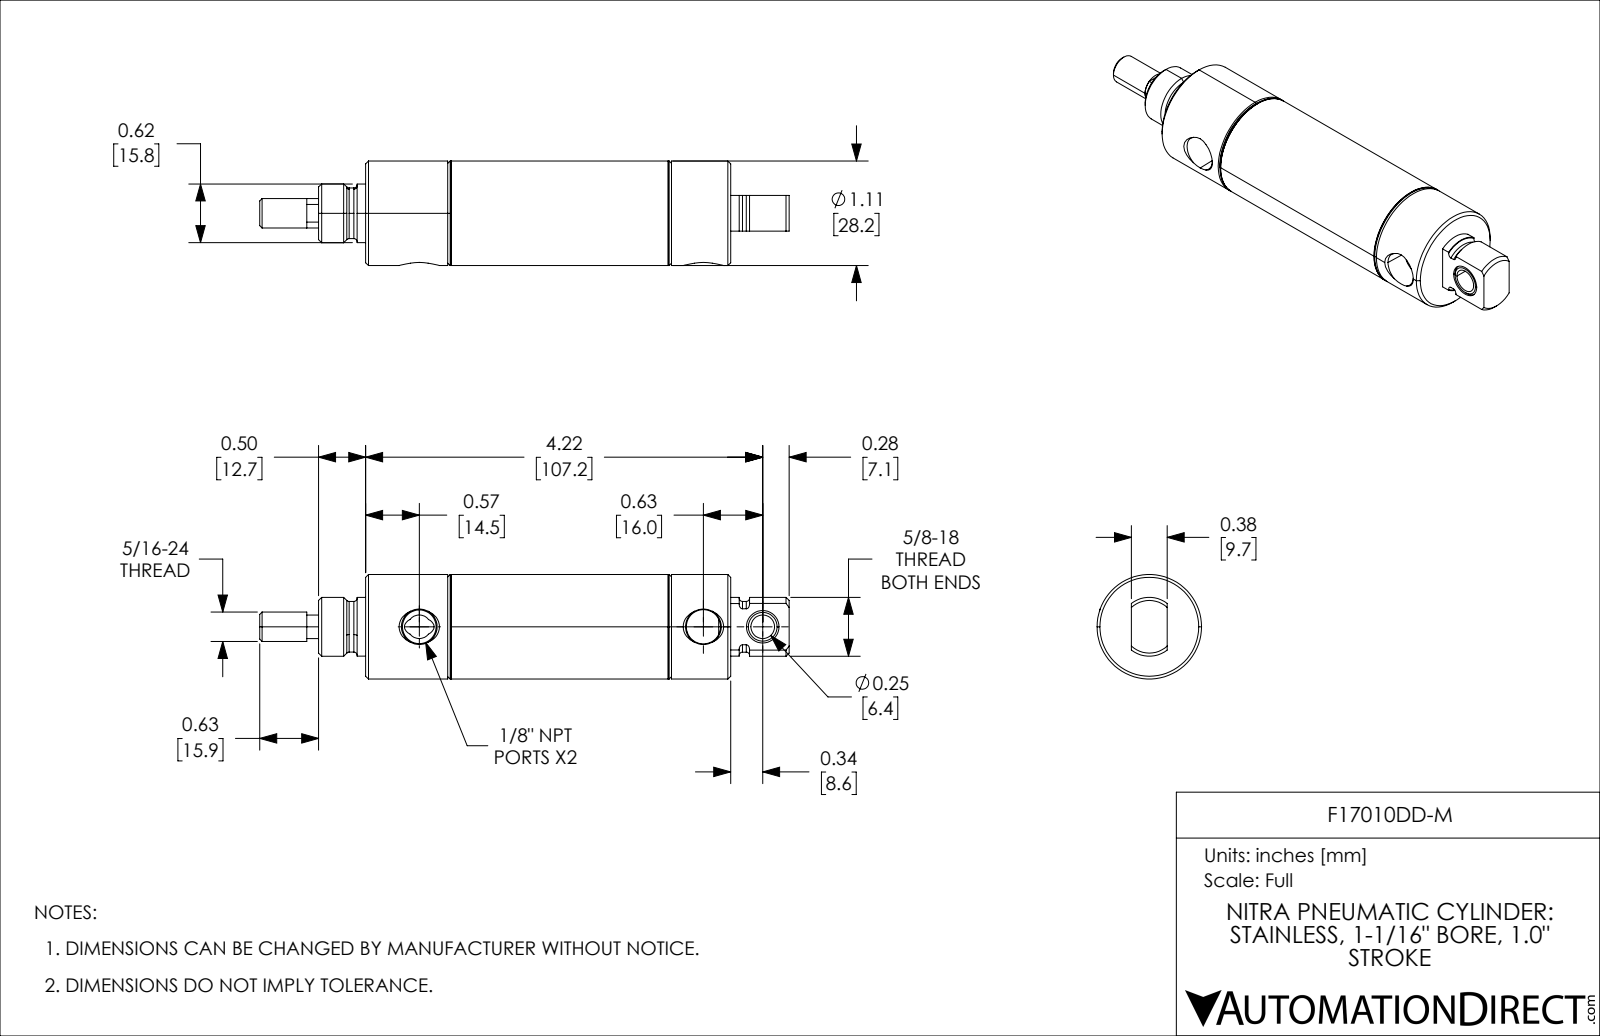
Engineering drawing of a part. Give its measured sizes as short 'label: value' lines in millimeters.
name: F17010DD-M; F17010DD-M_7; F17010DD-M_3; F17010DD-M_9 (+2 more)
written by: SolidWorks 2021 (CONFIG_CONTROL_DESIGN)
unit: mm
bodies: 5 solids, 156 faces (30 planar, 58 cylindrical, 68 other)
size: 142.88 × 28.19 × 28.19
volume: 48 173 mm³; area: 27 195 mm²
holes: 1× ⌀6.38, 1× ⌀8.53, 1× ⌀8.78, 1× ⌀9.25, 1× ⌀9.53, 1× ⌀19.05, 1× ⌀25.7
bosses: 1× ⌀28.19, 1× ⌀27.23, 1× ⌀15.88, 1× ⌀15.81, 1× ⌀13.68, 1× ⌀7.94, 1× ⌀7.92
rounds: 1× R3.17, 1× R6.84
face distances: 22.22, 25.4, 47.62, 69.95, 44.55, 22.33, 28.58, 53.98, 76.2, 98.53
hole spacings: 16.01
